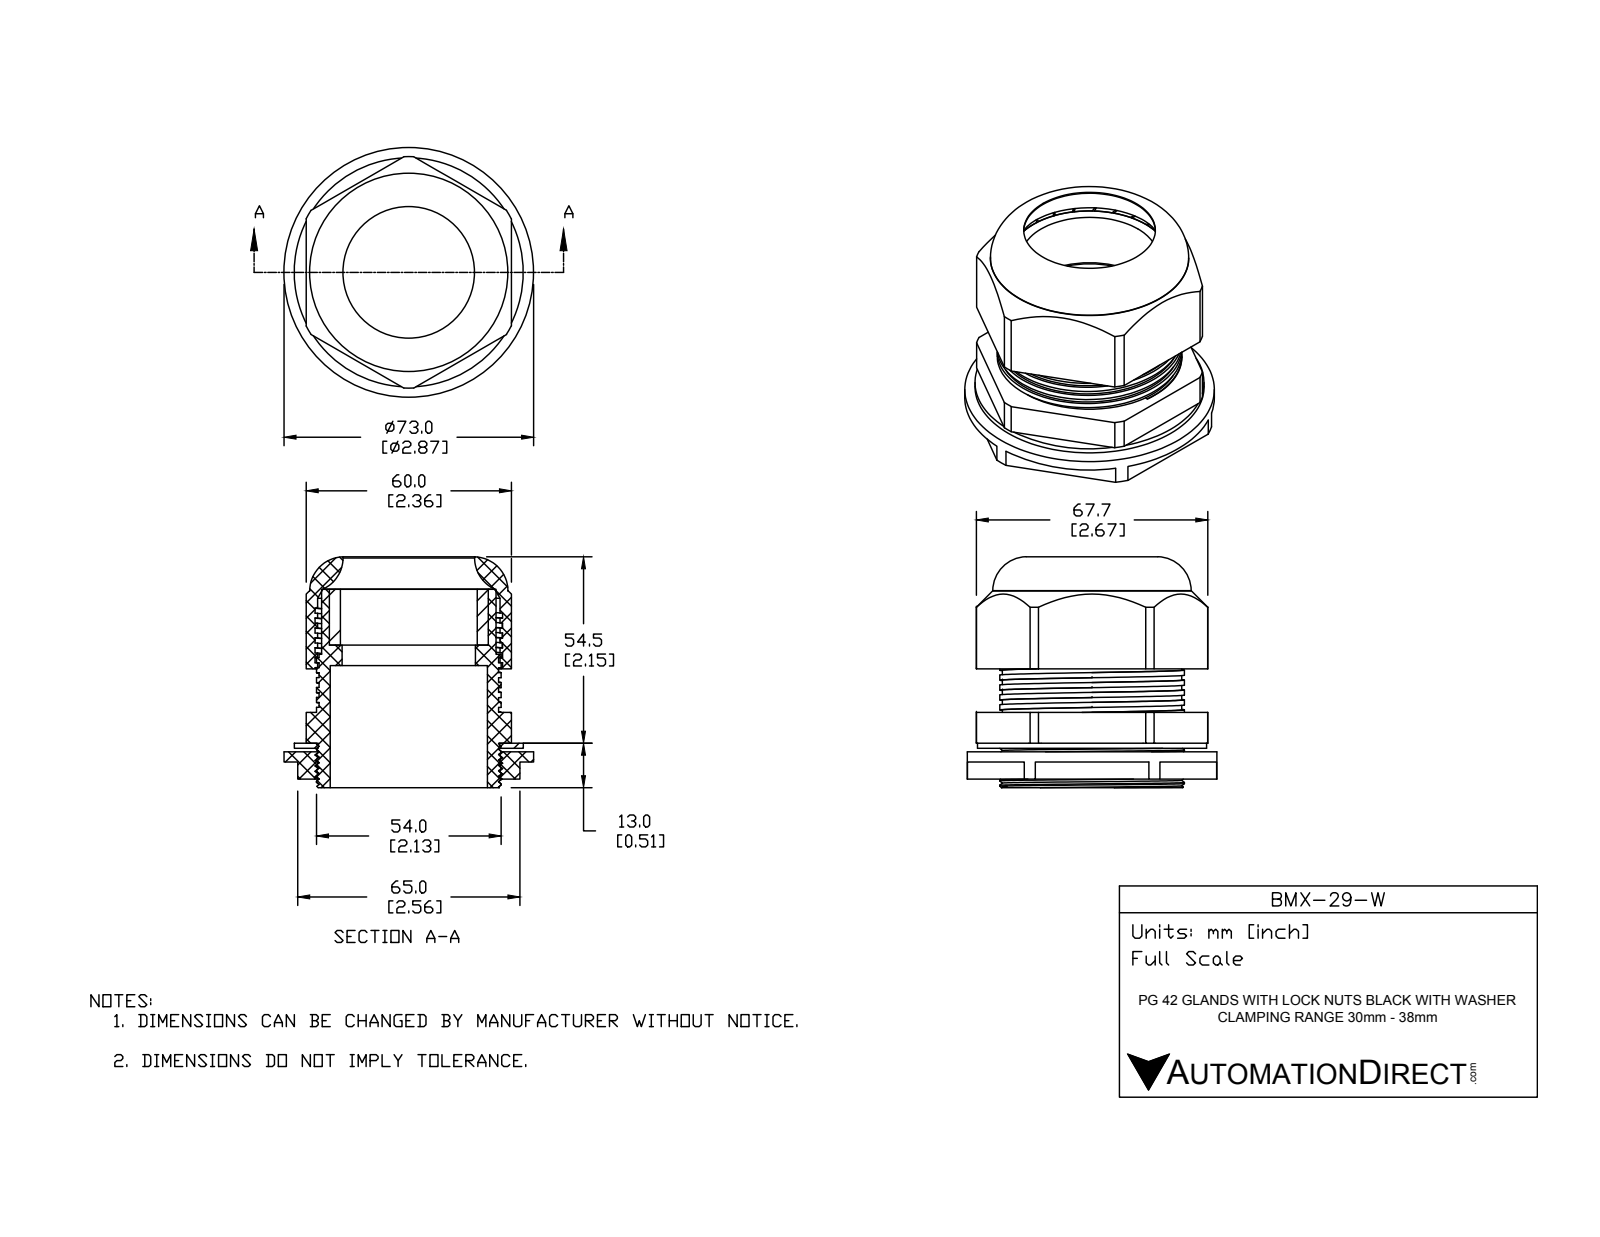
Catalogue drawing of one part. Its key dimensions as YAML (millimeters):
part_name: "BMX-29-W"
step_written_by: "SolidWorks 2015 (CONFIG_CONTROL_DESIGN)"
units: millimeters
bodies: {solids: 5, faces: 299, planar: 138, cylindrical: 140, other: 21}
overall_size: [73, 73, 67.5]
volume: 87876
surface_area: 57437
round_holes:
  - {diameter: 38.5, count: 1}
  - {diameter: 39, count: 1}
  - {diameter: 40, count: 1}
  - {diameter: 46.5, count: 1}
  - {diameter: 53, count: 1}
  - {diameter: 53.33, count: 1}
  - {diameter: 58, count: 1}
round_bosses_or_shafts:
  - {diameter: 73, count: 1}
  - {diameter: 67, count: 1}
  - {diameter: 54, count: 1}
  - {diameter: 51, count: 1}
  - {diameter: 46, count: 1}
partial_cylinders:
  - {radius: 33.85, count: 1}
face_to_face_distances: [2.5, 10.5, 60, 9, 23.25, 11.5, 8, 1, 1.5, 0.5]
